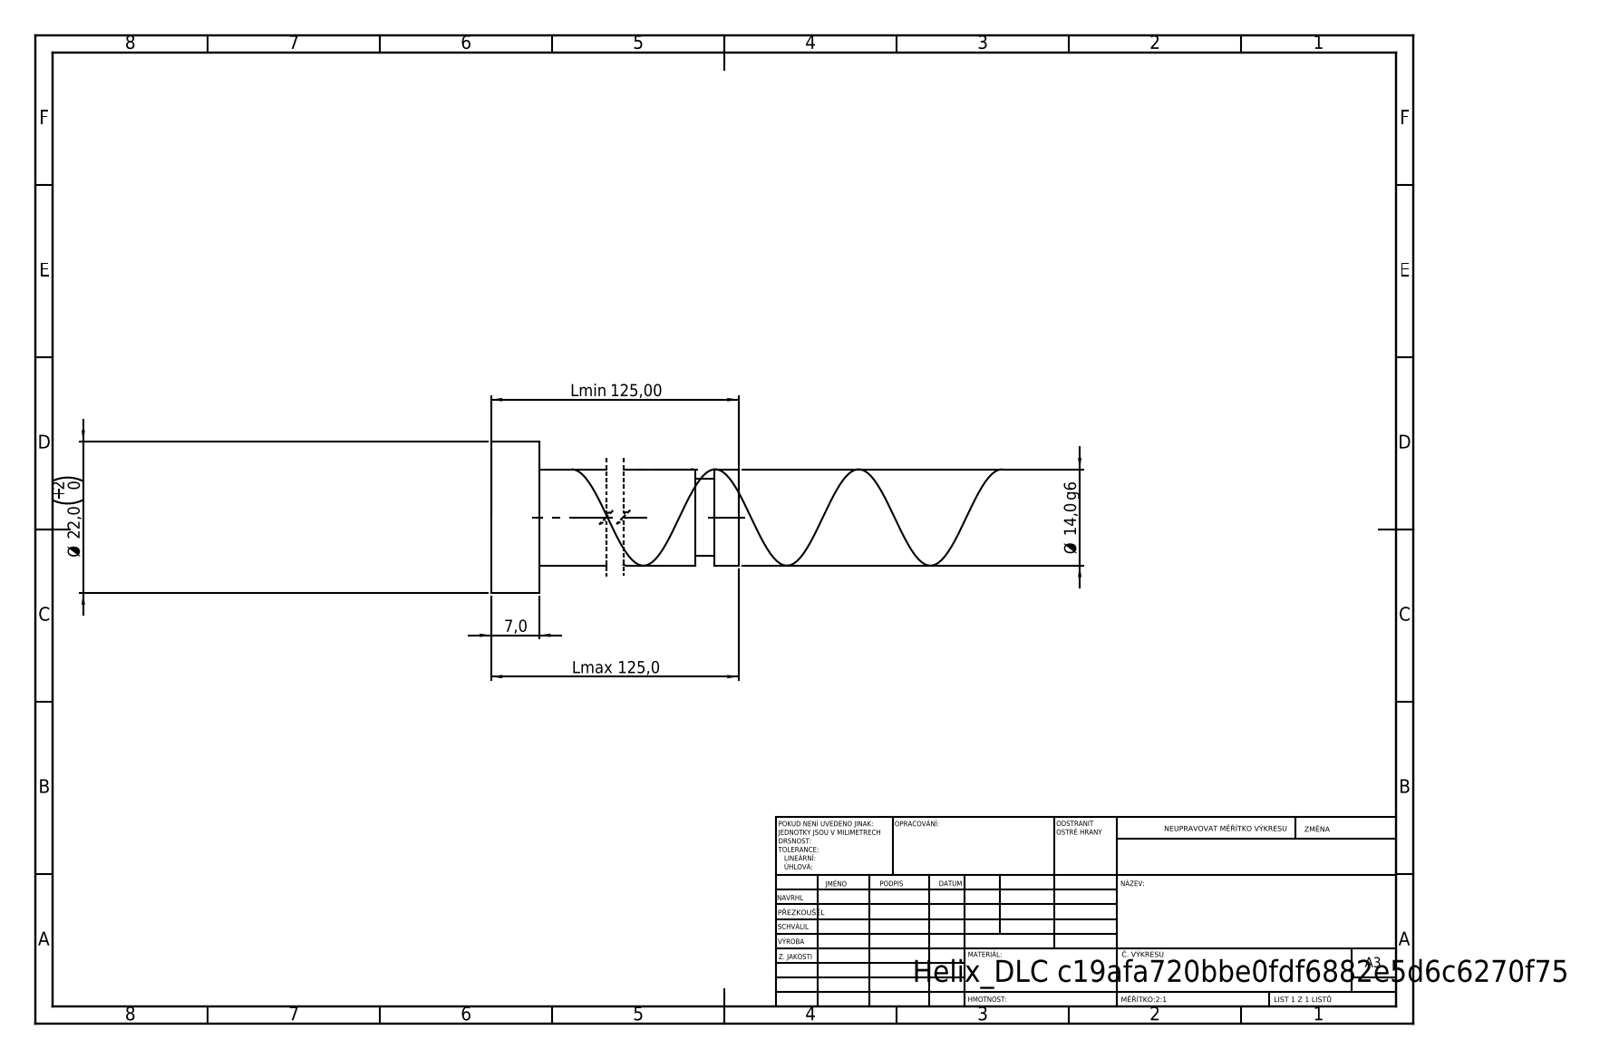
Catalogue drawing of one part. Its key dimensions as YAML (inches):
step_written_by: "SolidWorks 2019 (CONFIG_CONTROL_DESIGN)"
units: inches
bodies: {solids: 1, faces: 21, planar: 6, cylindrical: 14, other: 1}
overall_size: [4.921, 0.866, 0.866]
volume: 1.25
surface_area: 10.51
round_bosses_or_shafts:
  - {diameter: 0.866, count: 1}
  - {diameter: 0.551, count: 1}
  - {diameter: 0.441, count: 1}
face_to_face_distances: [0.276, 4.921, 4.646, 4.785, 4.509, 0.136, 4.675, 4.399, 0.11, 0.246]
